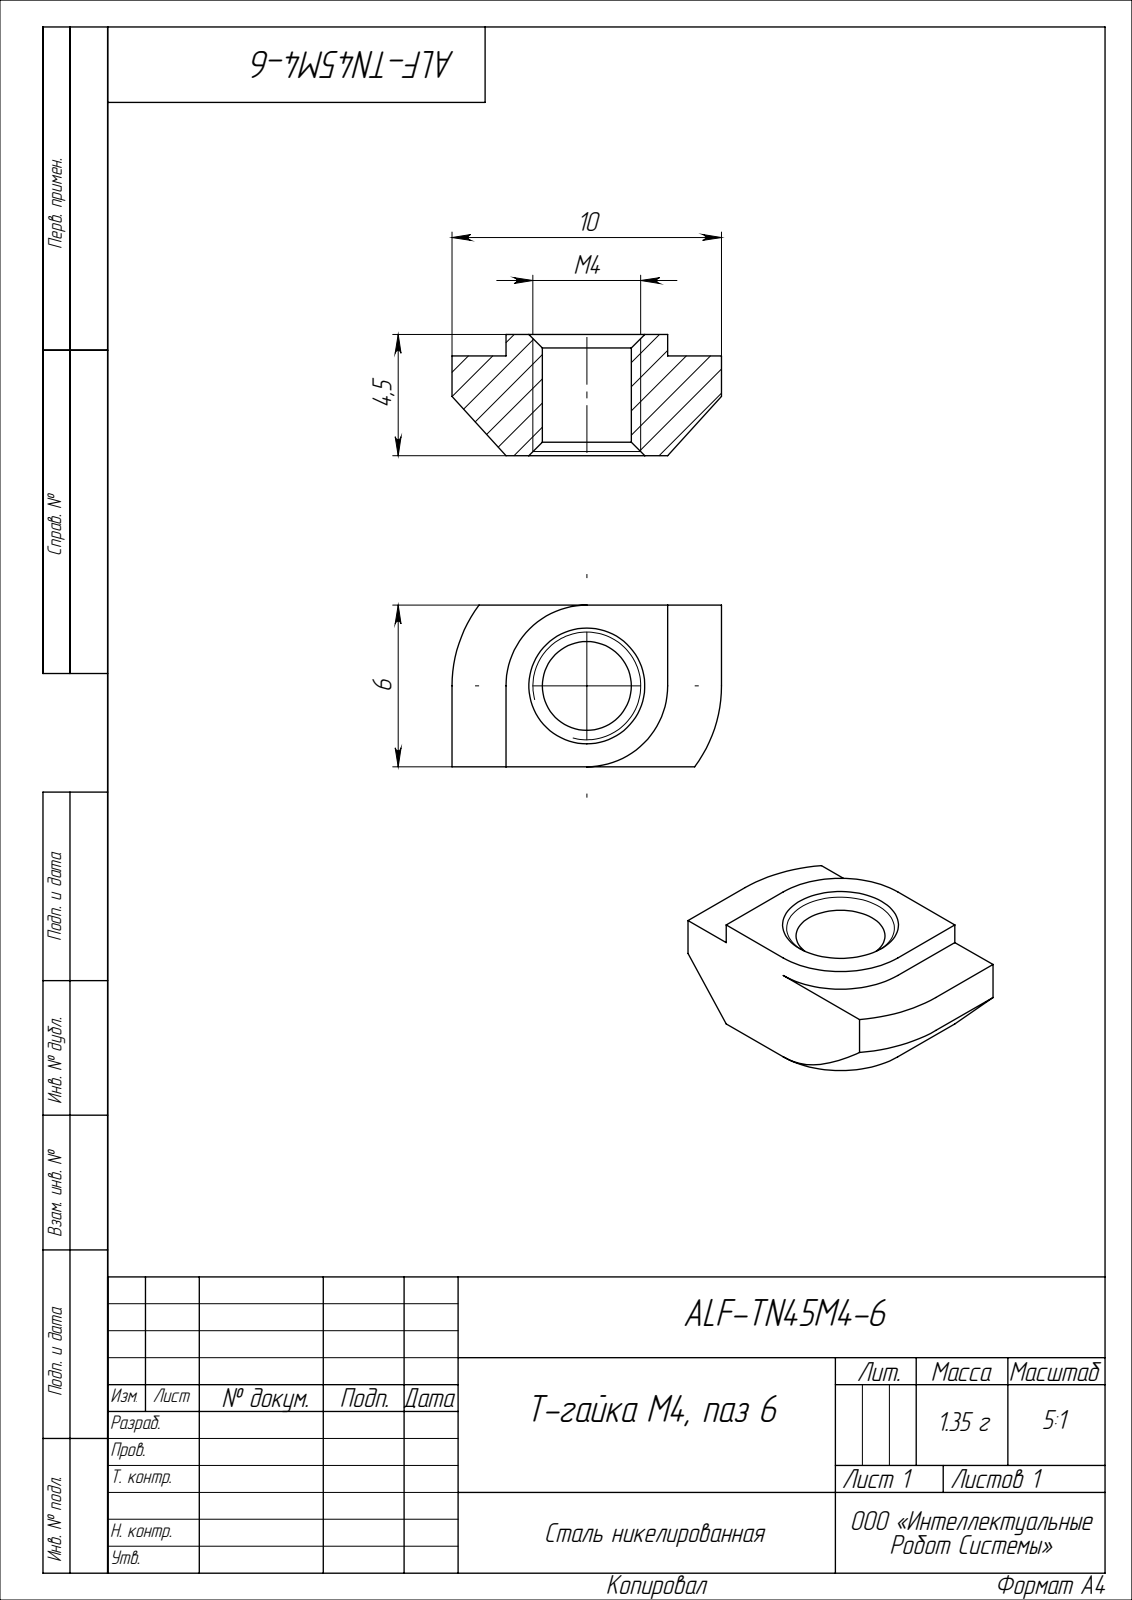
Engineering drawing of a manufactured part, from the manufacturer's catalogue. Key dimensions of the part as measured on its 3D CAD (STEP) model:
Part name (STEP PRODUCT): ALF-TN45М4-6
STEP written by: SolidWorks 2022 (CONFIG_CONTROL_DESIGN)
Units: millimetres
Bodies: 1 solid, 24 faces (12 planar, 6 cylindrical, 6 other)
Overall size (bounding box): 10 × 6 × 4.5
Volume: 171 mm³ · Surface area: 244 mm²
Round holes (diameter × count): ⌀3.3 ×1
Partial cylindrical surfaces — rounded edges, fillets, slot ends (radius × count): R3 ×1, R5 ×1
Main face-to-face distances: 6, 0.8, 3.7, 4.5, 2, 8, 10
